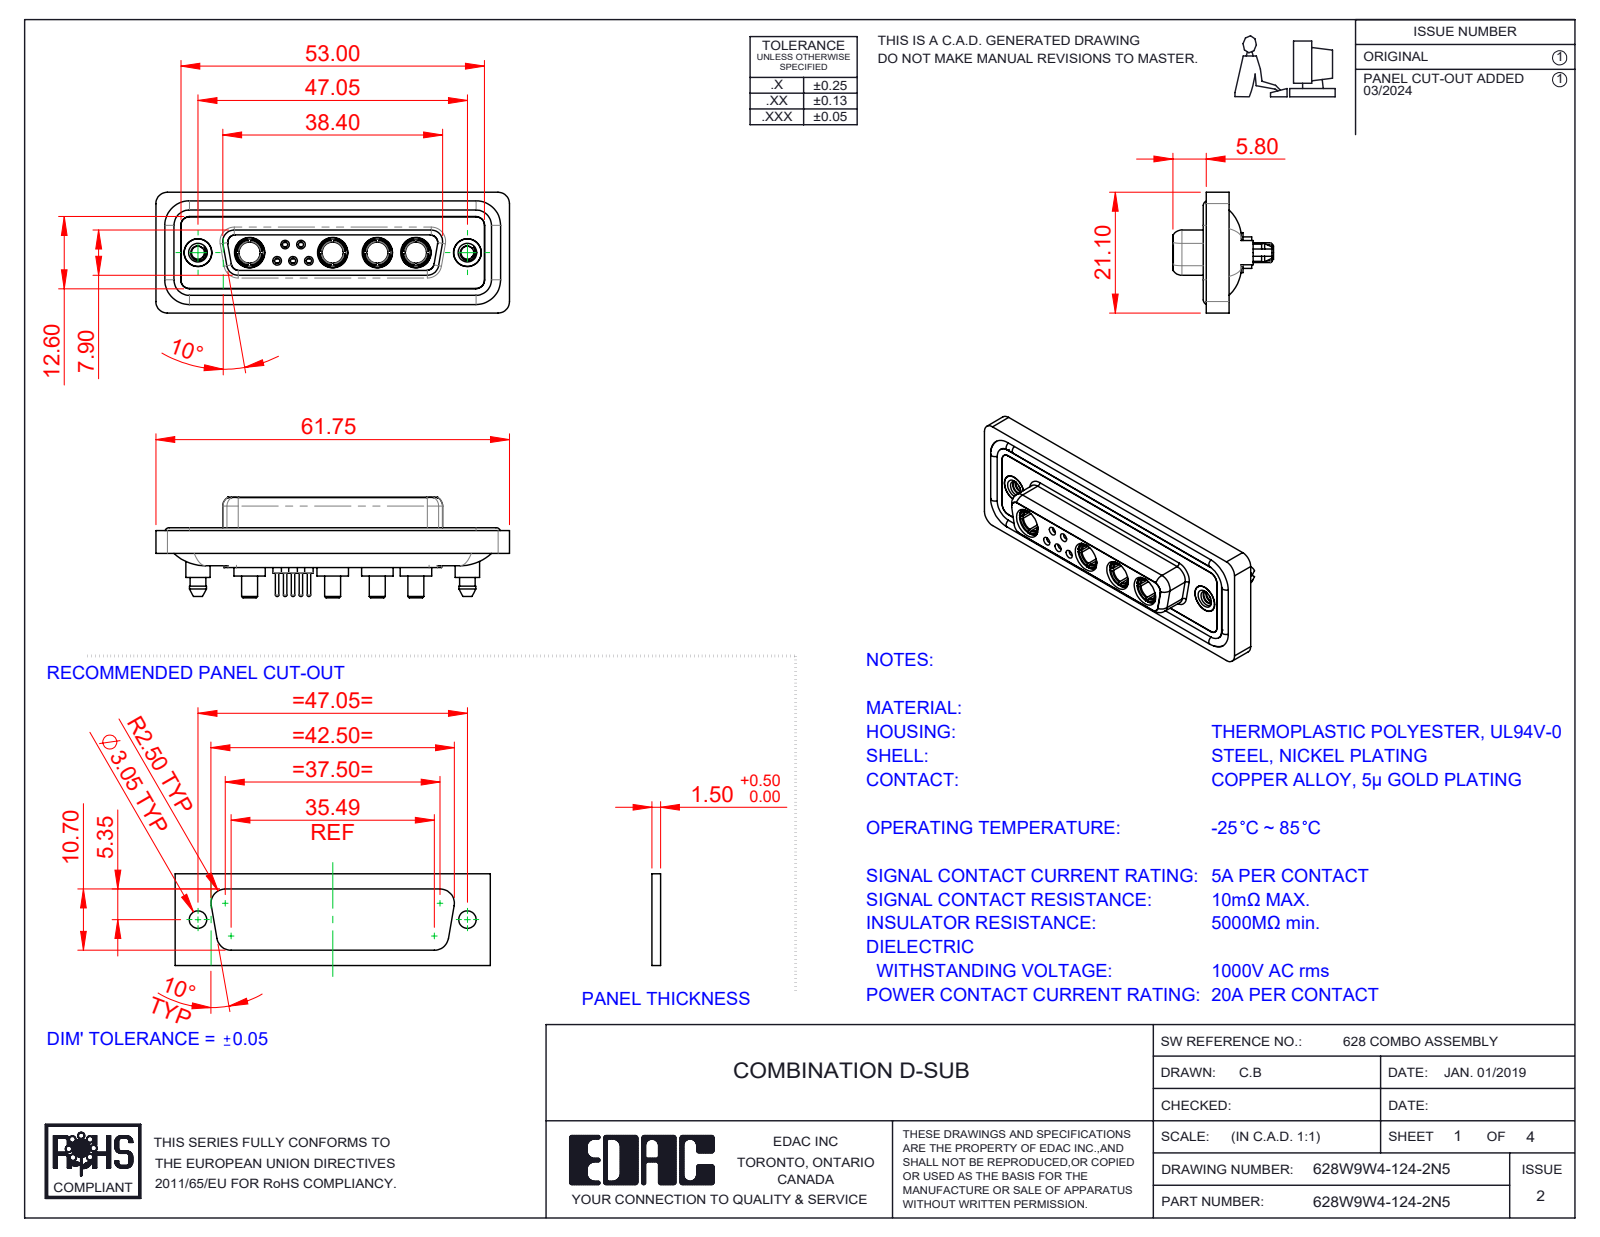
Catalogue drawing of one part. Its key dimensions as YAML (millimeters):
part_name: "628W9W4-124-2N5; 628Combo Waterproof Housing_25 Contacts; 628Combo Shell Front_25 Contacts; Power Socket_20A S (+5 more)"
step_written_by: "SolidWorks 2023 (CONFIG_CONTROL_DESIGN)"
units: millimeters
bodies: {solids: 20, faces: 1007, planar: 312, cylindrical: 407, other: 288}
overall_size: [61.75, 21.1, 17.55]
volume: 8357
surface_area: 13895
round_holes:
  - {diameter: 4.85, count: 6}
  - {diameter: 0.9, count: 5}
  - {diameter: 1.1, count: 5}
  - {diameter: 1.5, count: 5}
  - {diameter: 2, count: 5}
  - {diameter: 3.7, count: 4}
  - {diameter: 5.3, count: 4}
  - {diameter: 1.6, count: 3}
  - {diameter: 1.7, count: 2}
  - {diameter: 2.26, count: 2}
  - {diameter: 4, count: 2}
  - {diameter: 4.05, count: 2}
round_bosses_or_shafts:
  - {diameter: 1.6, count: 6}
  - {diameter: 2.2, count: 5}
  - {diameter: 0.6, count: 5}
  - {diameter: 5.5, count: 4}
  - {diameter: 5.2, count: 4}
  - {diameter: 4.96, count: 4}
  - {diameter: 4.75, count: 4}
  - {diameter: 3.75, count: 4}
partial_cylinders:
  - {radius: 1.5, count: 24}
  - {radius: 2, count: 18}
  - {radius: 1.6, count: 10}
  - {radius: 1.35, count: 8}
  - {radius: 0.25, count: 4}
  - {radius: 0.5, count: 4}
  - {radius: 0.6, count: 4}
  - {radius: 0.65, count: 4}
face_to_face_distances: [0.4, 1.8, 7.45, 5.65, 0.5, 7.05, 6.6, 1.6, 1.1, 2.9]
hole_center_spacings: [3.16, 2.77, 5.03, 2.76, 4.4, 5.02, 5.54, 5.73]
